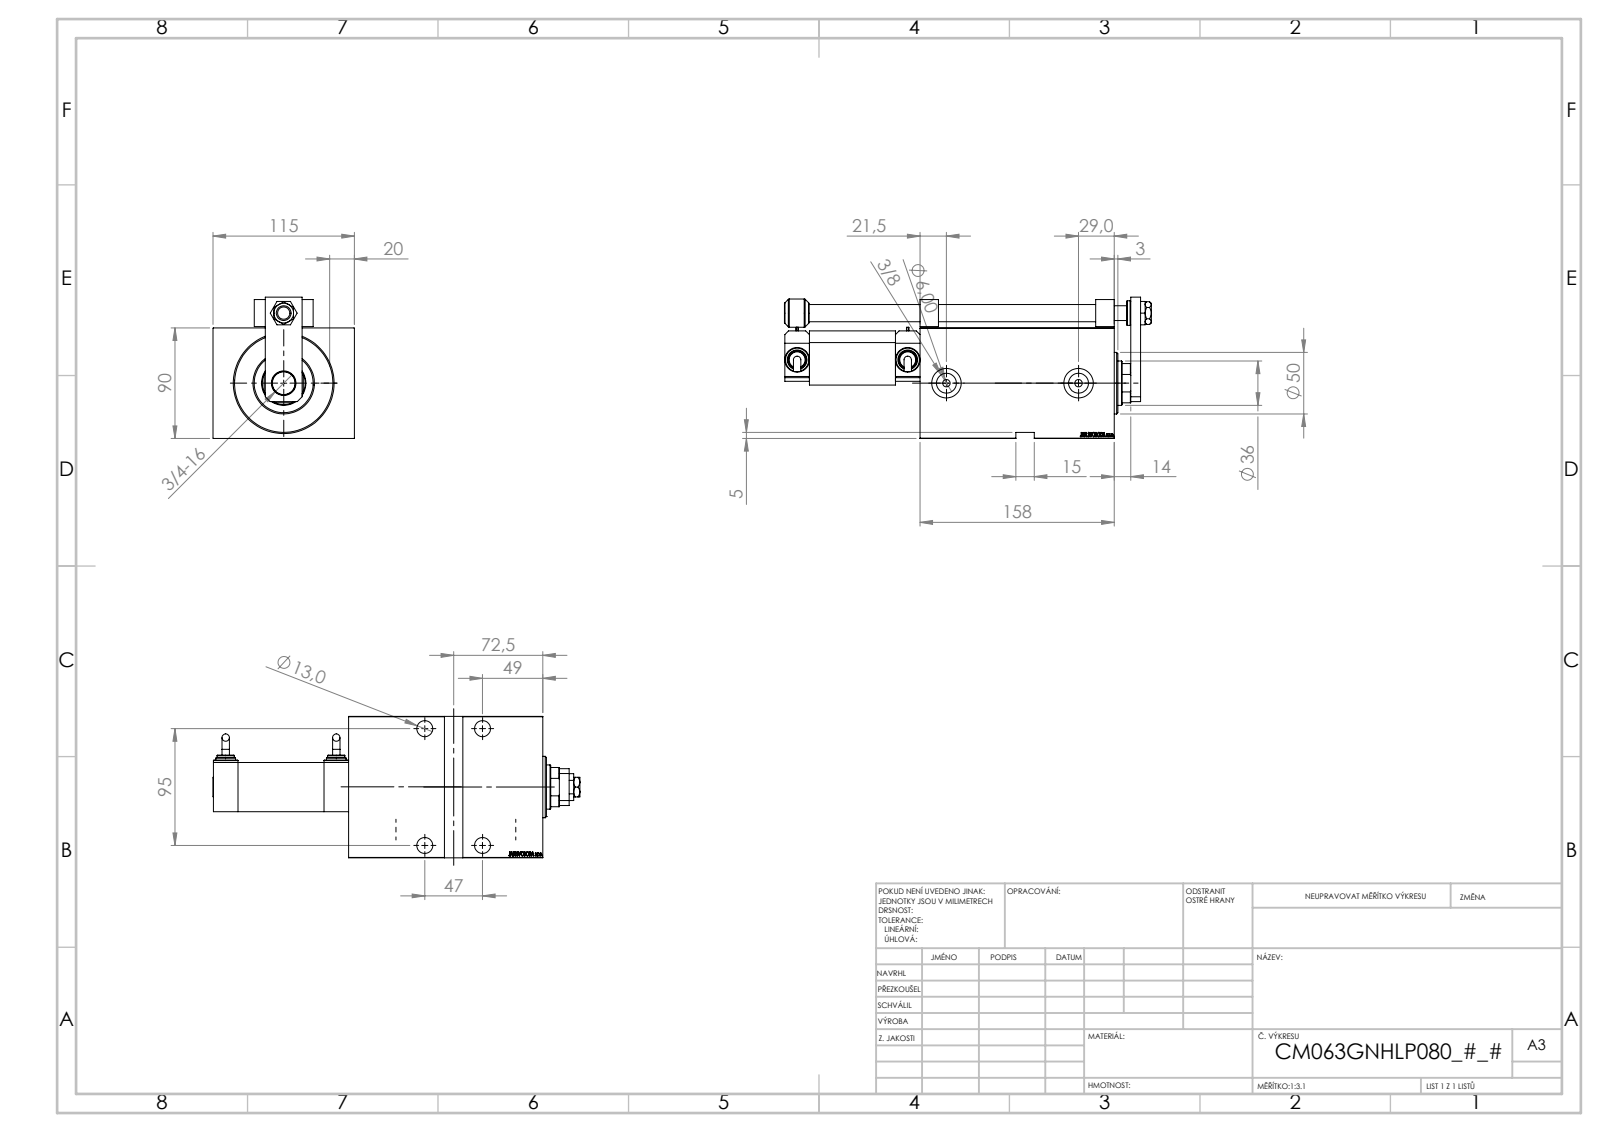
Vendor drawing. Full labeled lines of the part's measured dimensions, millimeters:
Part name (STEP PRODUCT): SWITCH P; V450CM_VC_G; NUT_D19_P; V450CM_G_Body (+7 more)
STEP written by: SolidWorks 2019 (CONFIG_CONTROL_DESIGN)
Units: millimetres
Bodies: 16 solids, 1116 faces (551 planar, 112 cylindrical, 453 other)
Overall size (bounding box): 298.5 × 115 × 115
Volume: 1 657 000 mm³ · Surface area: 236 427 mm²
Round holes (diameter × count): ⌀13 ×5, ⌀4 ×4, ⌀8 ×4, ⌀19 ×4, ⌀6 ×2, ⌀16.17 ×2, ⌀24 ×2, ⌀12 ×1, ⌀14 ×1, ⌀18.5 ×1, ⌀20 ×1, ⌀36 ×1
Round bosses / shafts (diameter × count): ⌀20 ×3, ⌀22 ×2, ⌀16 ×2, ⌀14 ×2, ⌀6 ×2, ⌀50 ×1, ⌀23 ×1
Partial cylindrical surfaces — rounded edges, fillets, slot ends (radius × count): R3 ×1, R17.5 ×1
Main face-to-face distances: 90, 115, 37.5, 5, 158, 77.5, 17.5, 140.5, 153, 135.5
Hole centre spacings: 20, 47, 55.93, 66.16, 70.91, 79.22, 95, 96.12
